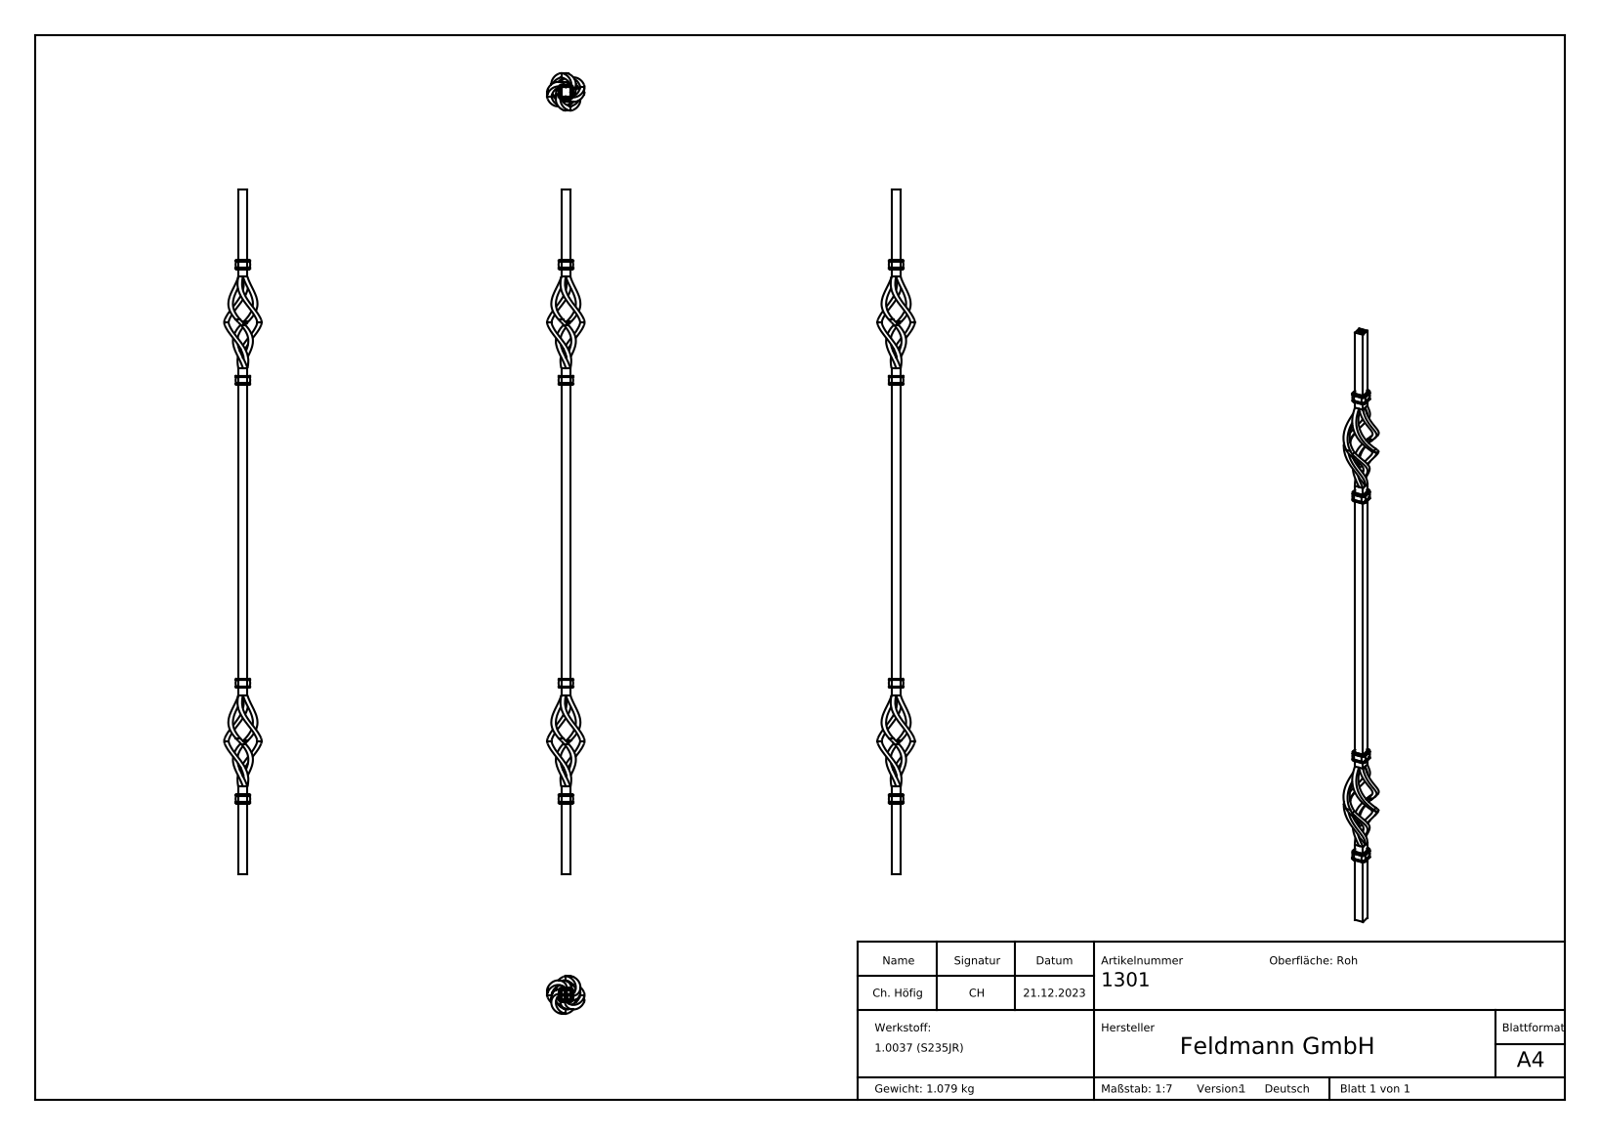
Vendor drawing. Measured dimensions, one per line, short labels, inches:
name: 1301
written by: SolidWorks 2018 (CONFIG_CONTROL_DESIGN)
unit: in
bodies: 1 solid, 813 faces (326 planar, 220 cylindrical, 267 other)
size: 35.433 × 1.934 × 1.934
volume: 8.438 in³; area: 99.31 in²
rounds: 64× R0.039, 36× R0.02, 16× R0.335, 12× R0.157, 8× R0.394
face distances: 0.472, 0.476, 0.48, 21.654, 5.984, 0.079, 0.394, 27.638, 15.669, 0.138
